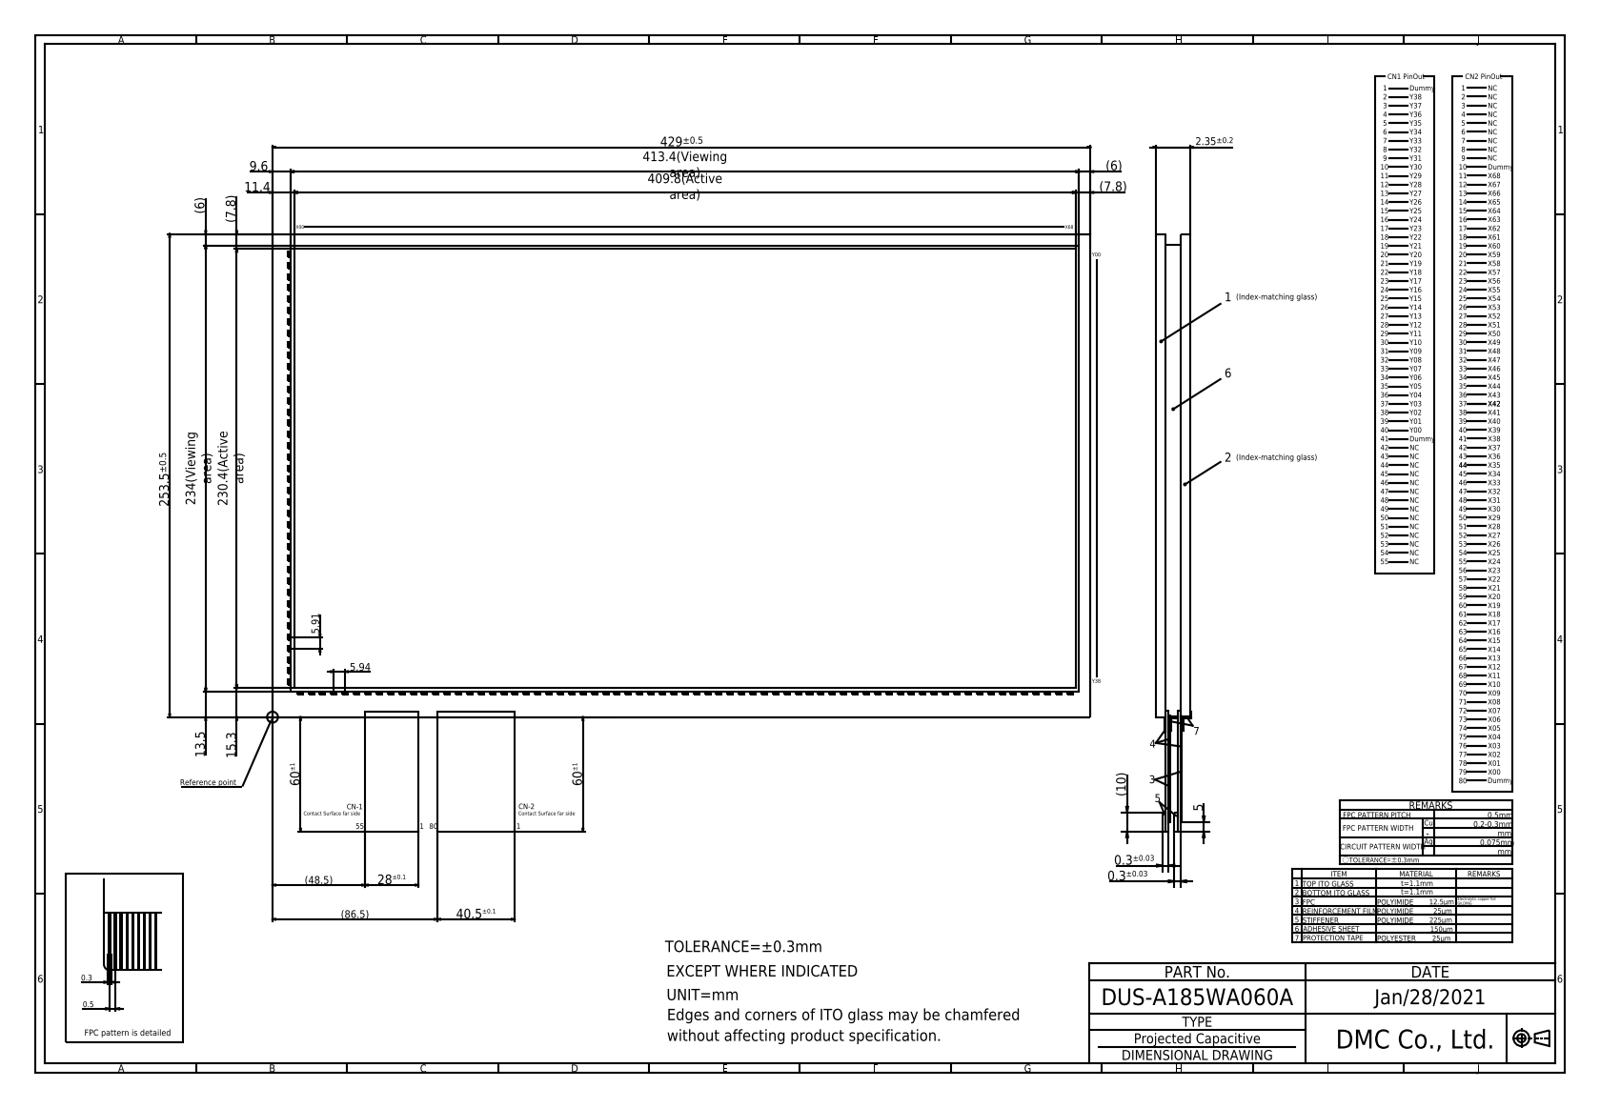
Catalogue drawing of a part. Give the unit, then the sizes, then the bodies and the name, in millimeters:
Units: millimetres
Overall size (bounding box): 600.6 × 364.2 × 2.35
Partial cylindrical surfaces — rounded edges, fillets, slot ends (radius × count): R0.2 ×4
Main face-to-face distances: 2.35, 1.1, 1.2, 1.15, 1.25, 1, 2.25, 253.5, 0.8, 0.7
Volume: 255 915 mm³ · Surface area: 229 276 mm²
Bodies: 1 solid, 578 faces (574 planar, 4 cylindrical, 0 other)
Part name (STEP PRODUCT): DUS-A185WA060A
STEP written by: Autodesk Inventor 2020 (CONFIG_CONTROL_DESIGN)
